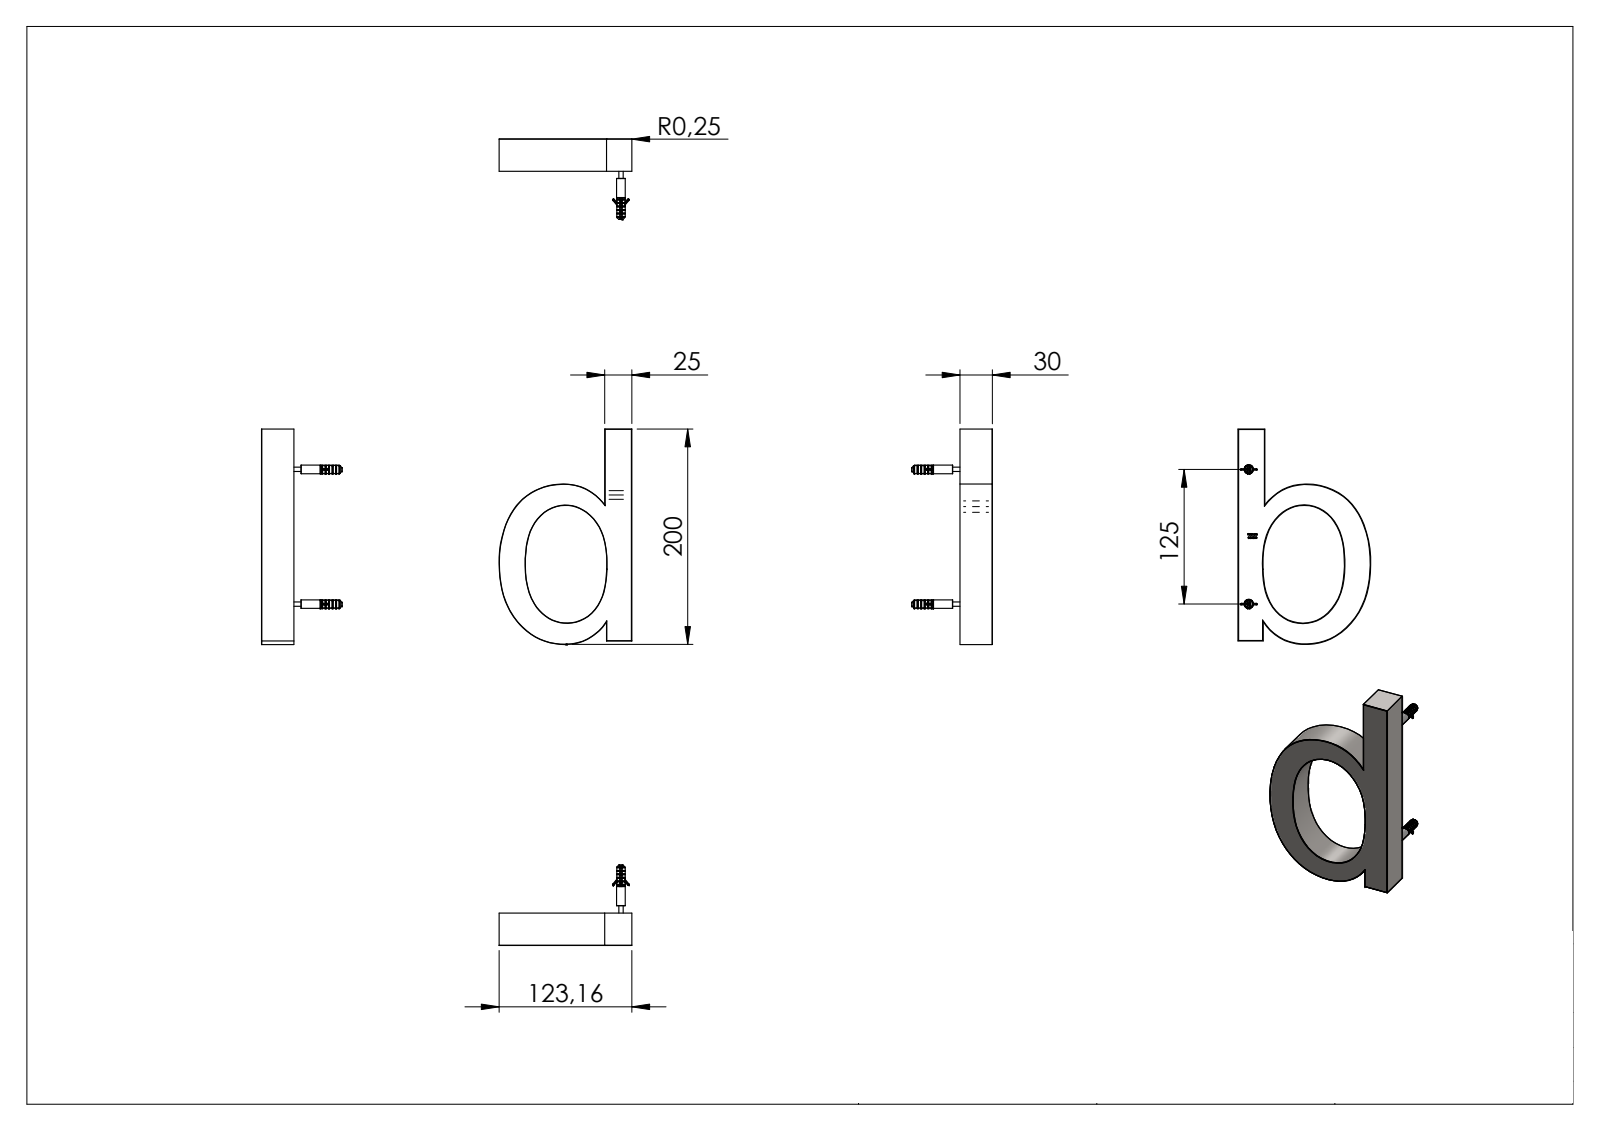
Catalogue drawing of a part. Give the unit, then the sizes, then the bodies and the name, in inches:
Units: inches
Overall size (bounding box): 7.875 × 6.013 × 4.849
Round holes (diameter × count): ⌀0.165 ×2
Round bosses / shafts (diameter × count): ⌀0.039 ×4, ⌀0.335 ×2, ⌀0.315 ×2, ⌀0.307 ×2, ⌀0.276 ×2, ⌀0.264 ×2, ⌀0.197 ×2, ⌀0.157 ×2
Partial cylindrical surfaces — rounded edges, fillets, slot ends (radius × count): R0.02 ×40, R0.008 ×34, R0.01 ×5
Main face-to-face distances: 0.079, 0.02, 0.965, 0.984, 0.945, 7.729, 0.064, 0.9, 7.749, 7.709
Hole centre spacings: 4.921
Volume: 2.394 in³ · Surface area: 124.9 in²
Bodies: 5 solids, 1129 faces (257 planar, 301 cylindrical, 571 other)
Part name (STEP PRODUCT): 042-HN-X Teil1_042-HN-D Teil1; 042-HN-D; 042-HN-X Teil3_042-HN-X Teil3; 042-HN-X Teil2_042-HN-X Teil2
STEP written by: SolidWorks 2015 (CONFIG_CONTROL_DESIGN)
